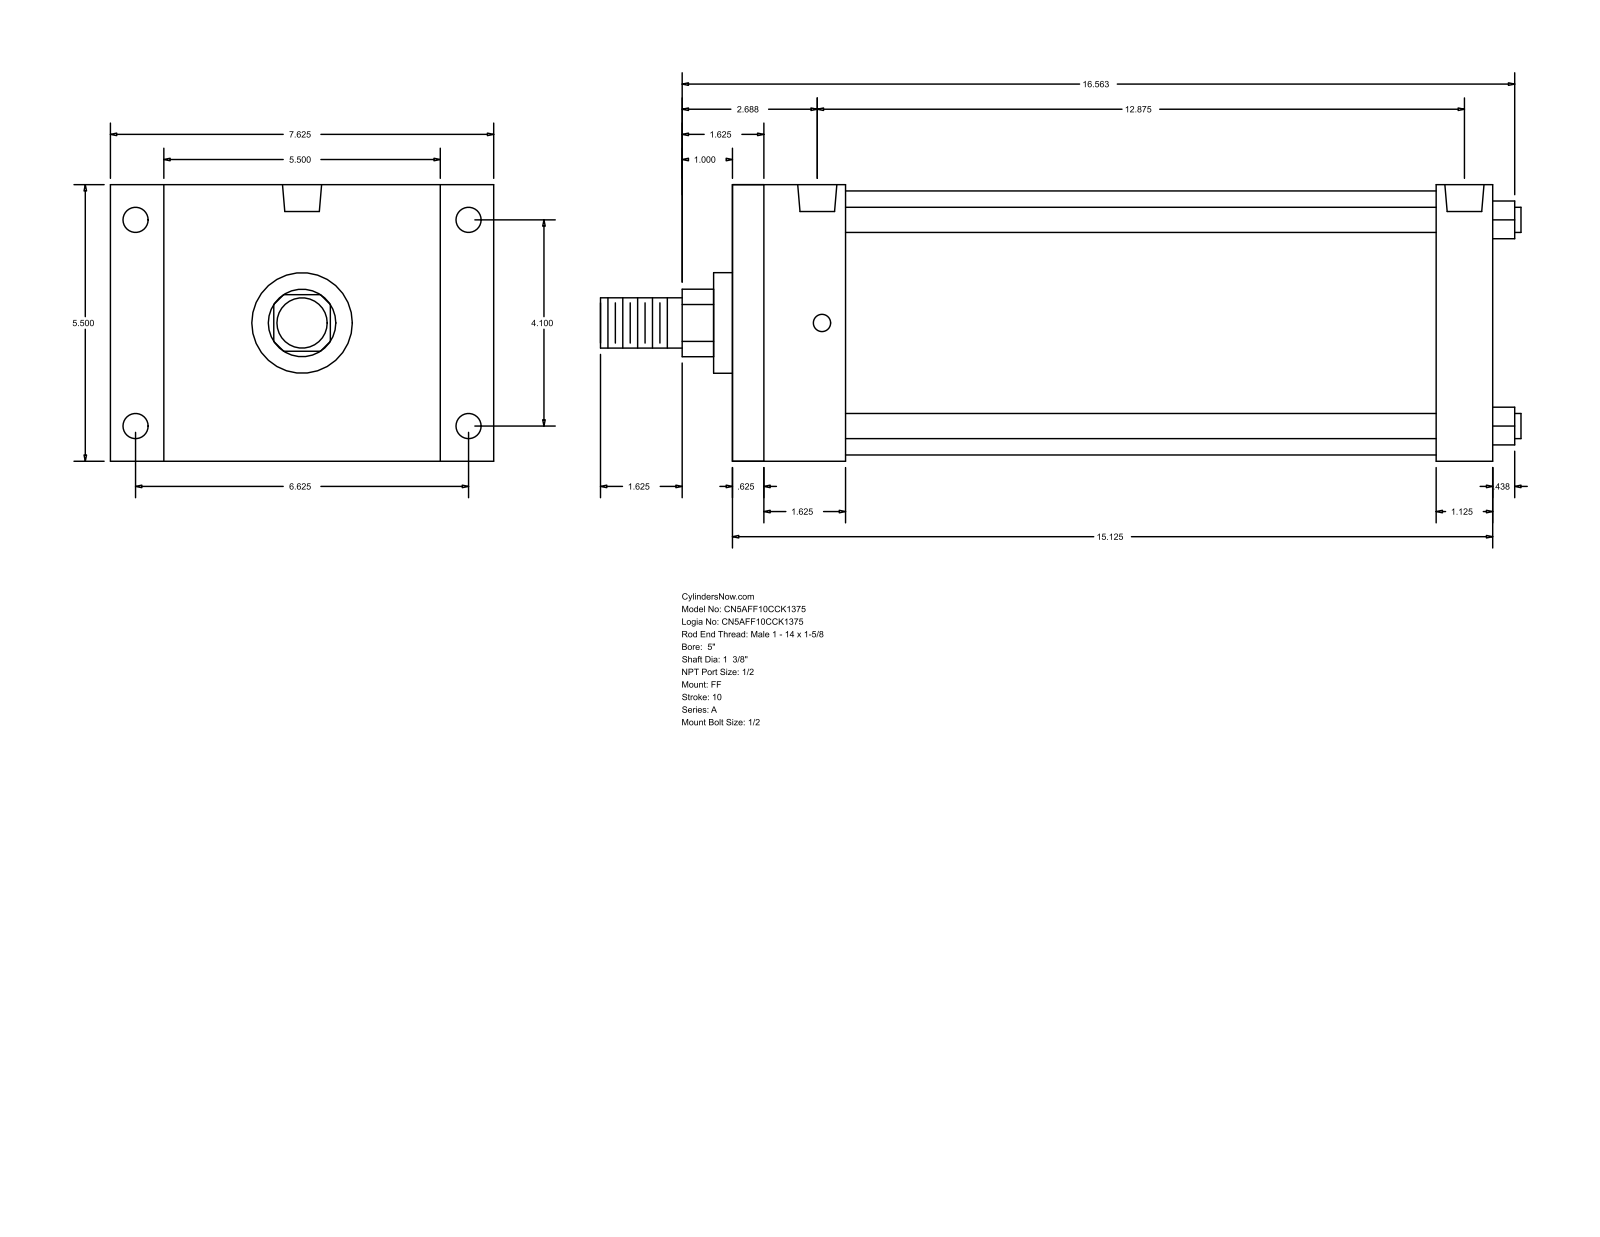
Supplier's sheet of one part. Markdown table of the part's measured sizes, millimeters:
| quantity | value |
| --- | --- |
| part name | A_FF__0500_1.375 |
| STEP written by | GSSL Pune (CONFIG_CONTROL_DESIGN) |
| units | millimeters |
| bodies | 0 solids, 92 faces (64 planar, 28 cylindrical, 0 other) |
| overall size | 465.14 × 193.68 × 139.7 |
| round holes (diameter × count) | 8.73 × 4, 12.7 × 4, 19.77 × 2 |
| round bosses / shafts (diameter × count) | 12.7 × 4, 133.35 × 1, 50.8 × 1, 34.92 × 1, 25.4 × 1 |
| partial cylindrical surfaces (radius × count) | 17.06 × 1 |
| main face-to-face distances | 139.7, 384.17, 368.3, 15.87, 57.15, 28.57, 355.6, 339.73, 41.28, 298.45 |
| hole center spacings | 2.39, 104.14, 168.28, 197.9, 322.25, 324.64, 327.03 |
